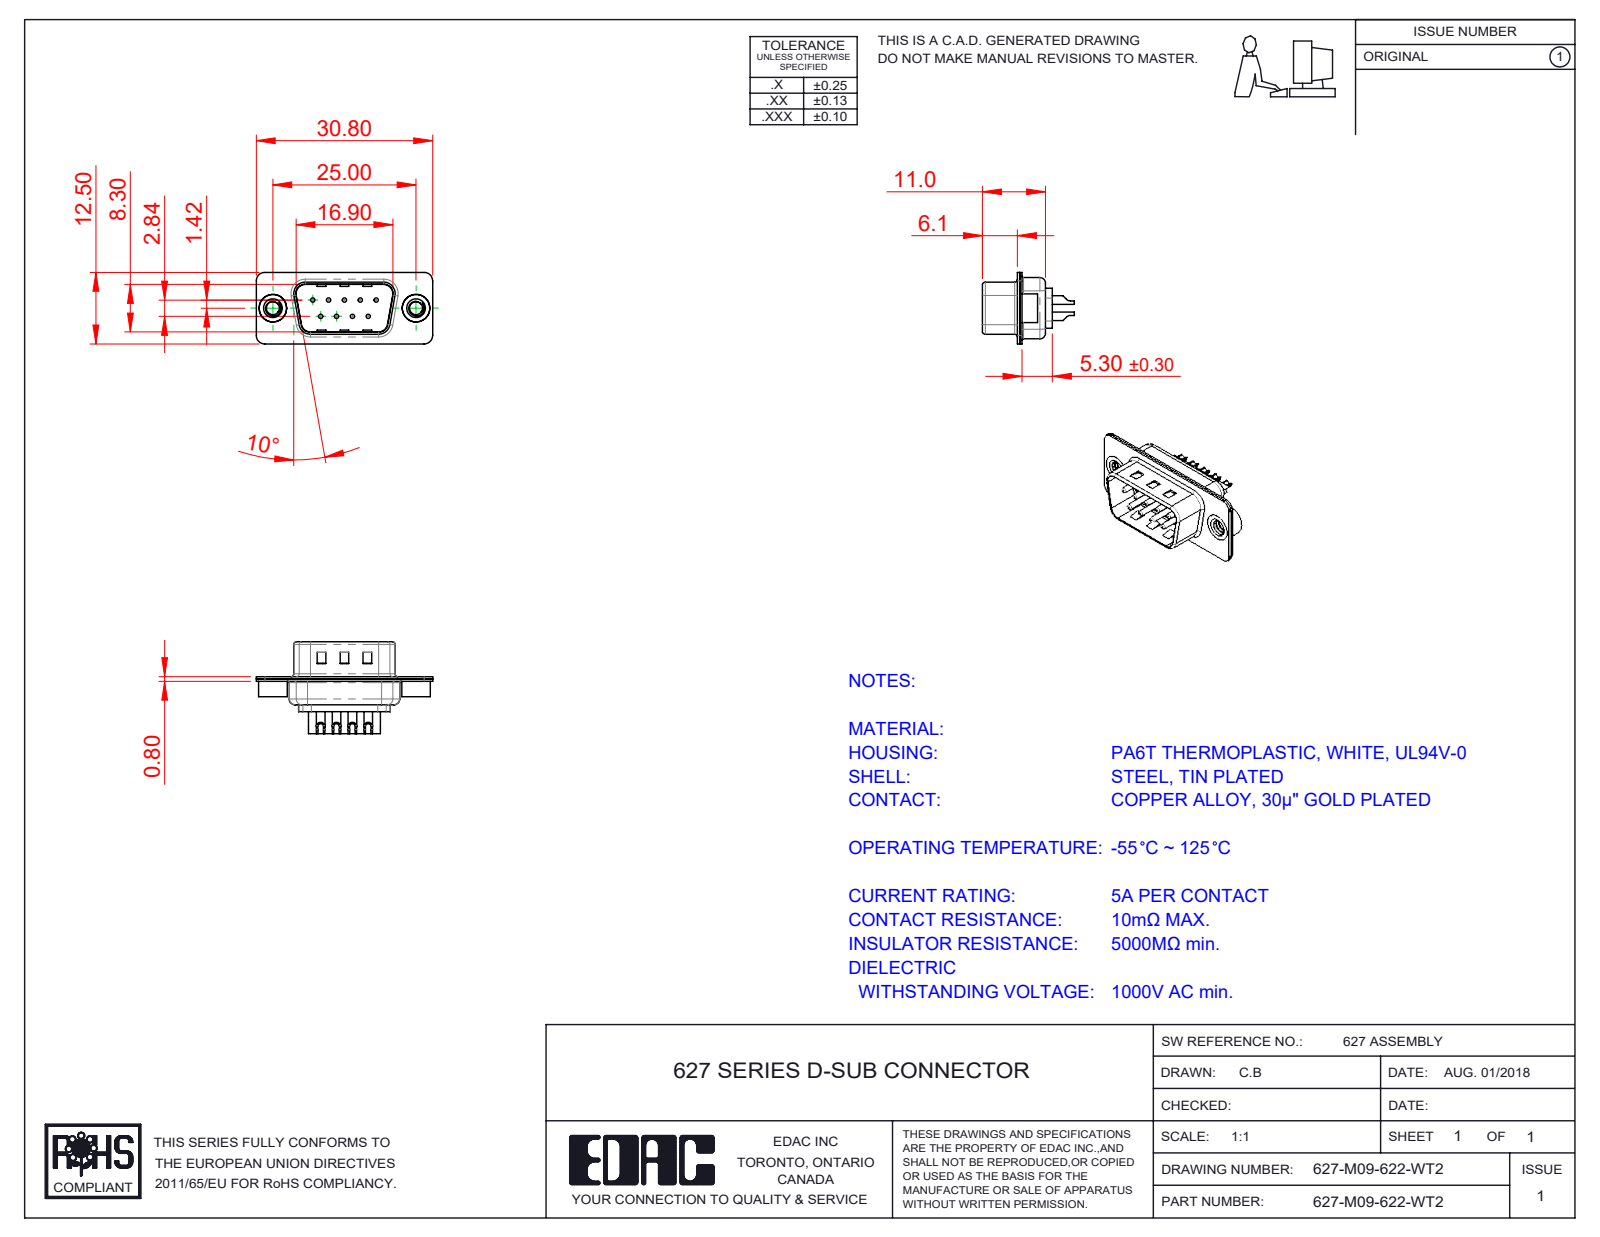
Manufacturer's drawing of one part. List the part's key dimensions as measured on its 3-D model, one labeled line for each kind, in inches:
Part name (STEP PRODUCT): 627-M09-622-WT2; 627M Contact Row 1_22; 627M 4-40 Threaded Rivet; 627M Contact Row 2_22 (+3 more)
STEP written by: SolidWorks 2020 (CONFIG_CONTROL_DESIGN)
Units: inches
Bodies: 14 solids, 637 faces (188 planar, 273 cylindrical, 176 other)
Overall size (bounding box): 1.213 × 0.632 × 0.492
Volume: 0.081 in³ · Surface area: 5.67 in²
Round holes (diameter × count): ⌀0.03 ×9, ⌀0.039 ×9, ⌀0.063 ×9, ⌀0.079 ×9, ⌀0.089 ×2, ⌀0.157 ×2, ⌀0.189 ×2
Round bosses / shafts (diameter × count): ⌀0.059 ×9, ⌀0.197 ×2, ⌀0.193 ×2
Partial cylindrical surfaces — rounded edges, fillets, slot ends (radius × count): R0.059 ×16, R0.079 ×12, R0.02 ×8, R0.063 ×8, R0.039 ×6, R0.01 ×4, R0.024 ×4, R0.026 ×4
Main face-to-face distances: 0.016, 0.031, 0.374, 0.358, 0.343, 0.026, 0.39, 0.047, 0.03, 0.014
Hole centre spacings: 0.124, 0.109, 0.218, 0.198, 0.198, 0.327, 0.28, 0.294
